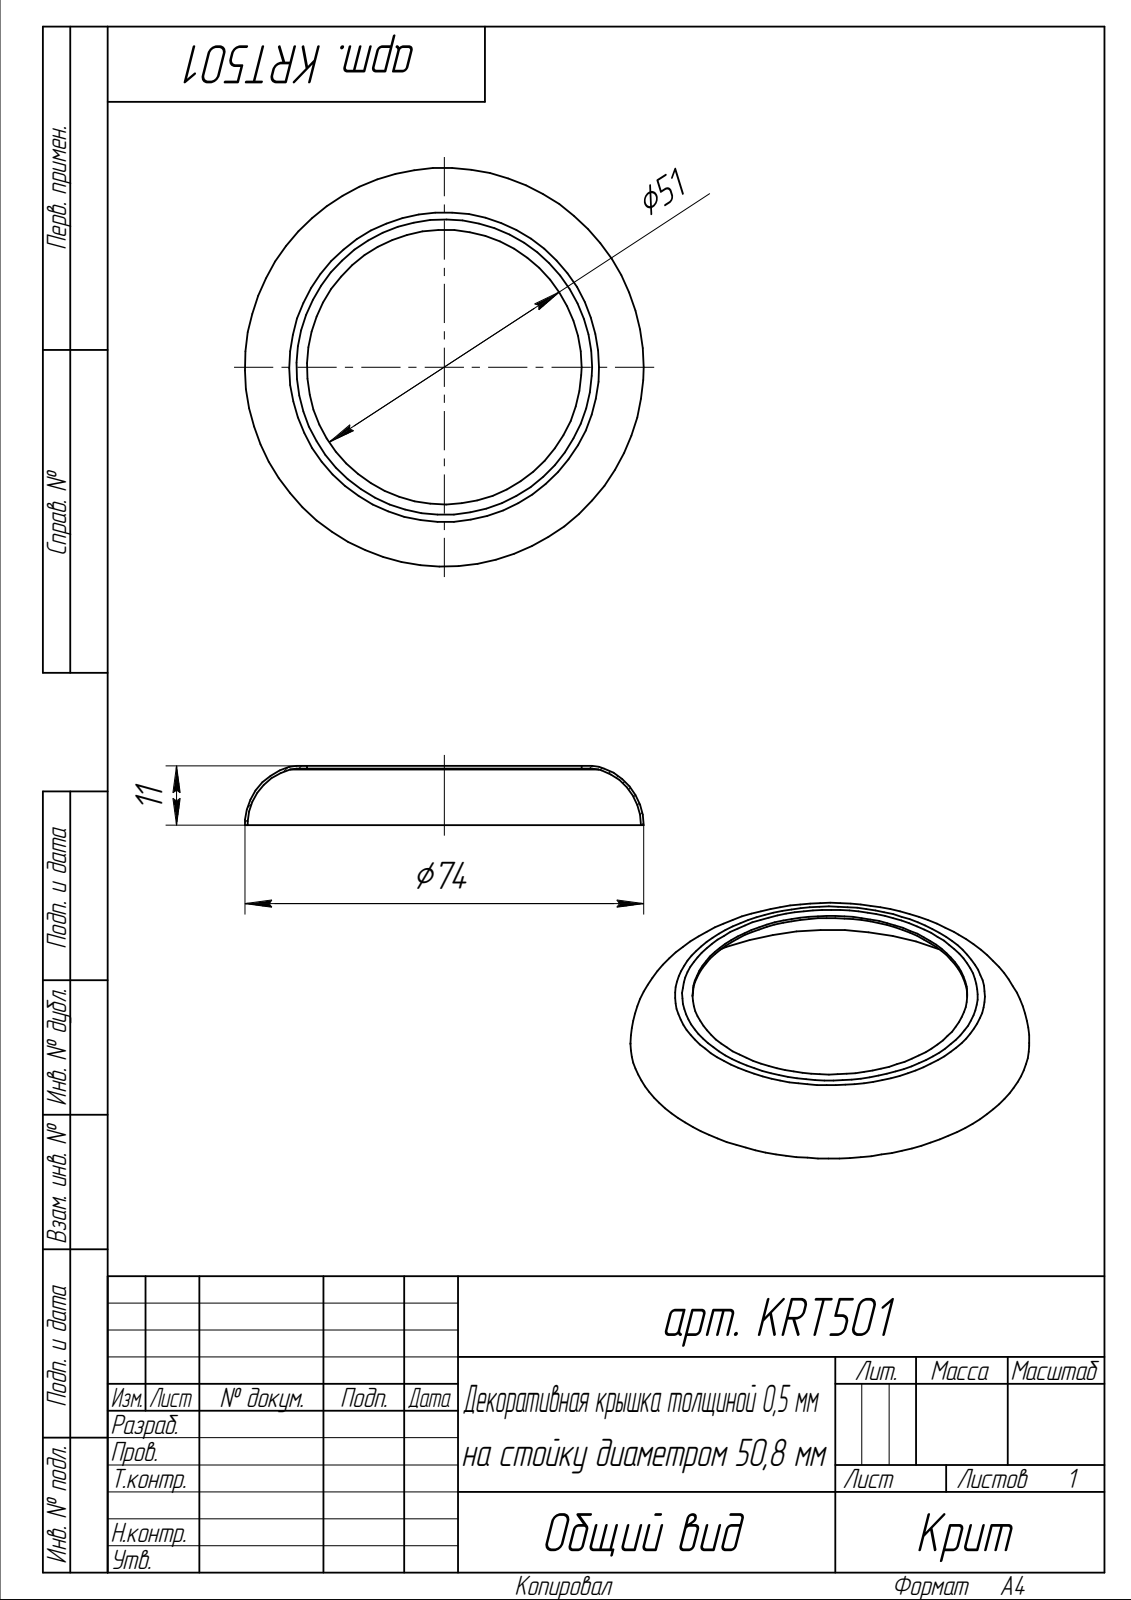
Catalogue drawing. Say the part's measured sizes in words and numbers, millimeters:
The part is named "арт. KRT501". Its 3-D file was written by "SolidWorks 2014 (AUTOMOTIVE_DESIGN)". It is 1 solid with 13 faces: 3 planar, 2 cylindrical and 8 other. Overall it measures 74 by 74 by 11 millimeters. Its volume is 1 795 cubic millimeters and its surface area 7 375 square millimeters. Round holes: 1 of diameter 51. The main face-to-face distances are 0.5, 10.5, 11.
